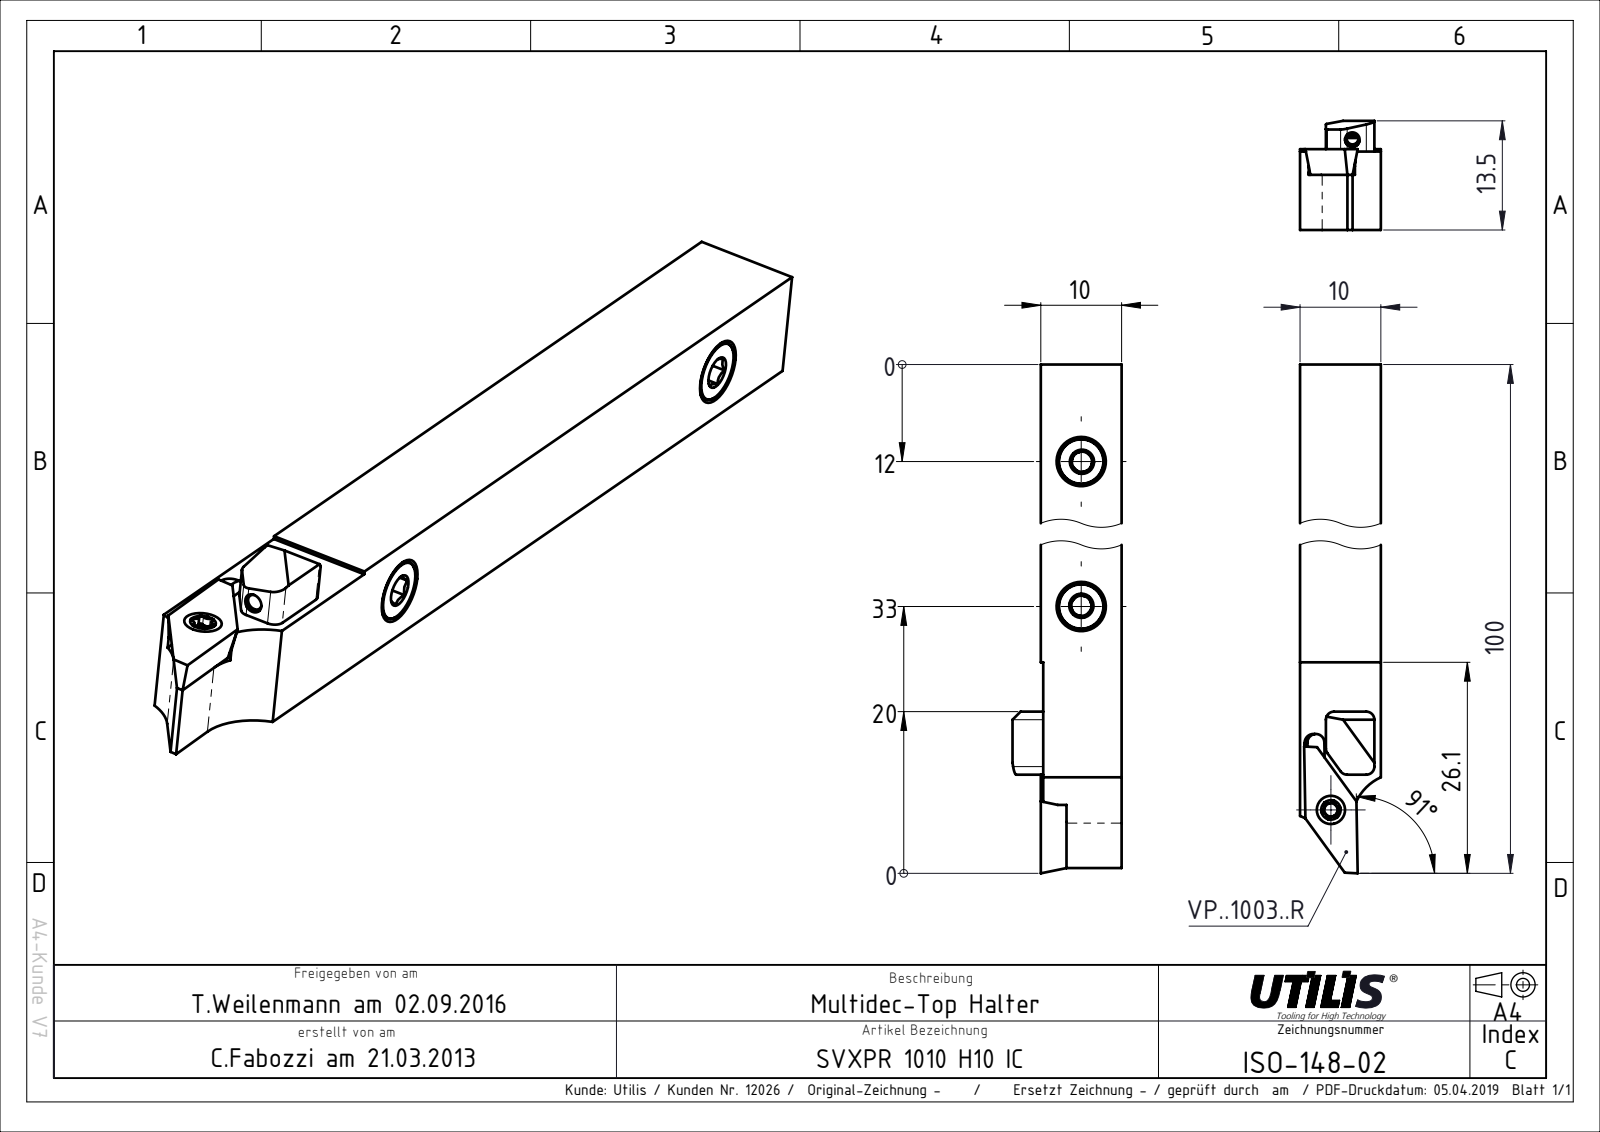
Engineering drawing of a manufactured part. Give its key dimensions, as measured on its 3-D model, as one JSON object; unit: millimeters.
{"part_name": "ISO-148-02", "step_written_by": "SolidWorks 2016 (AUTOMOTIVE_DESIGN)", "units": "millimeters", "bodies": {"solids": 1, "faces": 52, "planar": 42, "cylindrical": 9, "other": 1}, "overall_size": [100, 13.5, 10], "volume_mm3": 9473, "surface_area_mm2": 4165, "partial_cylinders_radius": [[1, 5], [6.1, 2], [1.05, 1]], "face_to_face_distances": [10, 9.7, 9.2, 0.8, 80, 3.2, 6, 6.8, 5.33, 13.5]}
